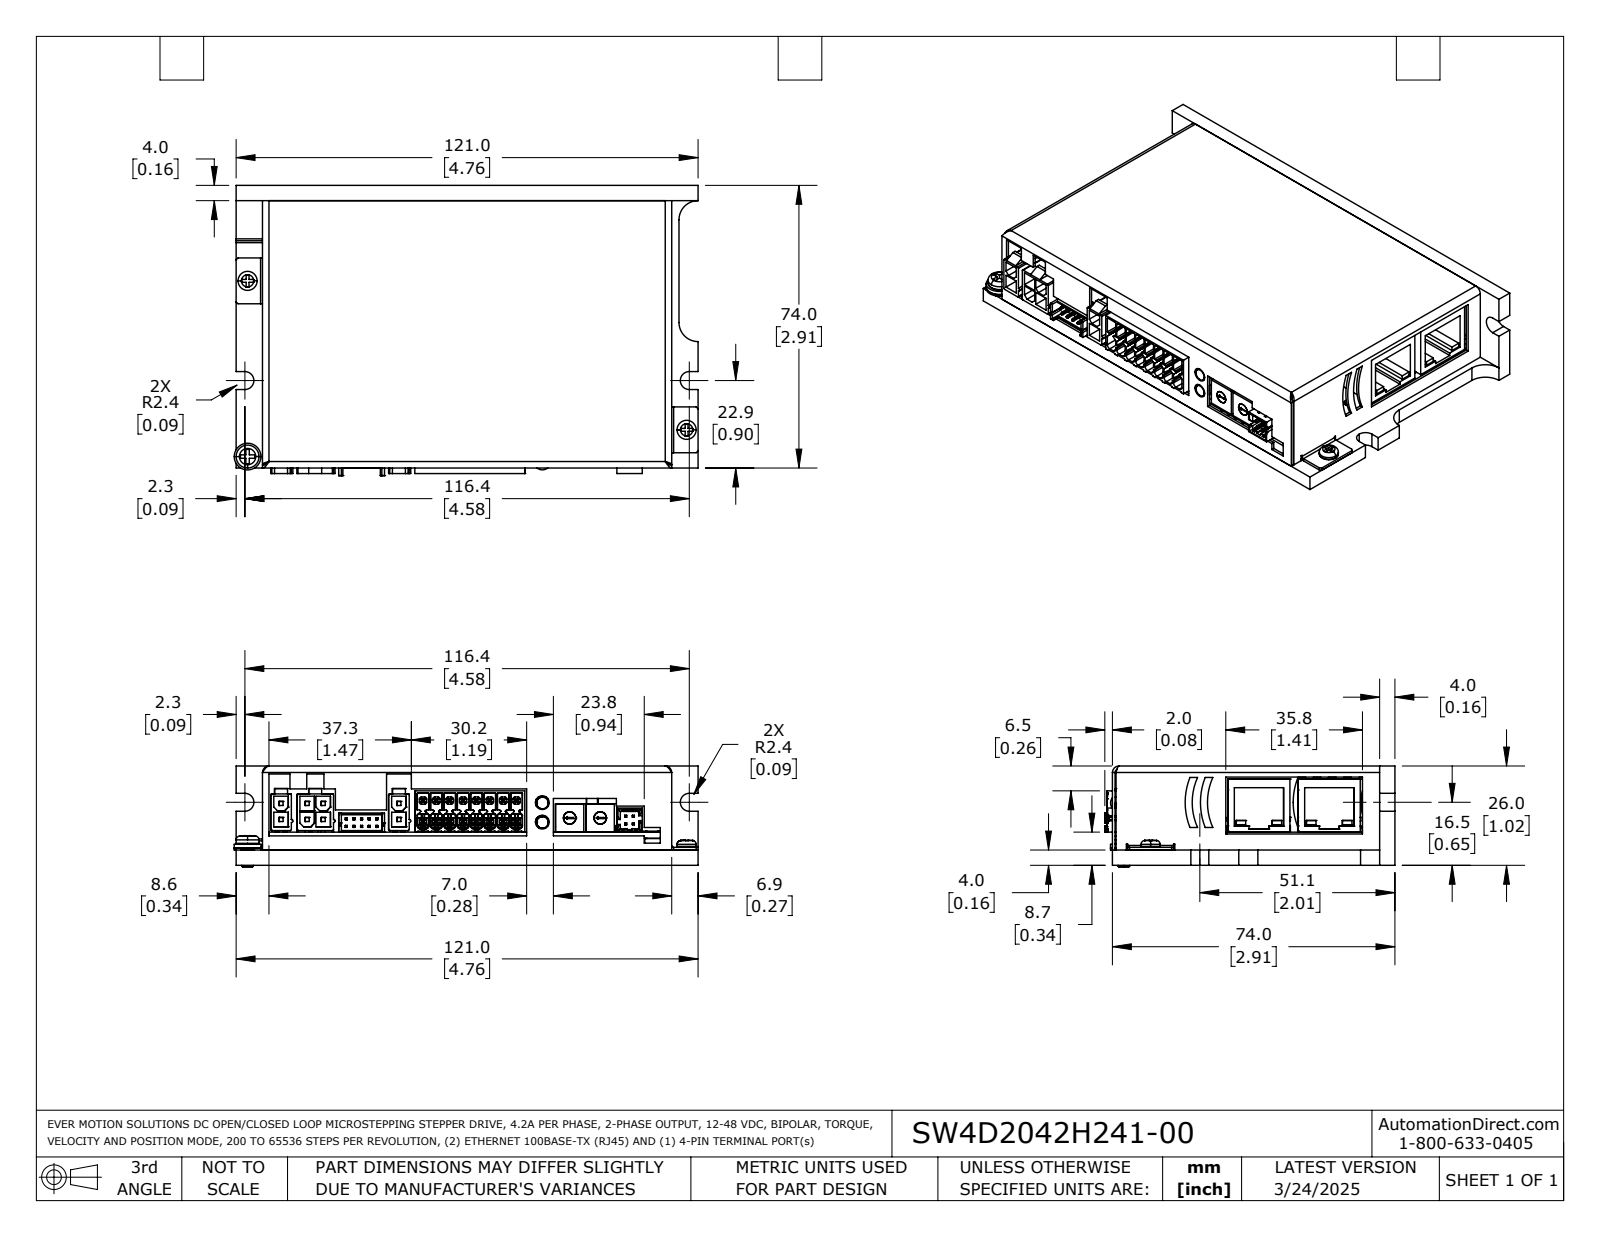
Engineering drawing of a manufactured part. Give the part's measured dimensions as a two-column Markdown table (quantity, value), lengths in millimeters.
| quantity | value |
| --- | --- |
| part name | SW4D2042H241-00C0680 |
| STEP written by | SolidWorks 2021 (AUTOMOTIVE_DESIGN) |
| units | millimeters |
| bodies | 21 solids, 3502 faces (2322 planar, 988 cylindrical, 192 other) |
| overall size | 121.5 × 76 × 26.5 |
| volume | 77 350 mm³ |
| surface area | 78 190 mm² |
| round holes (diameter × count) | 0.8 × 20, 0.9 × 16, 1.4 × 16, 0.9 × 14, 1 × 8, 1.3 × 8, 1.8 × 8, 3.2 × 7, 1.6 × 4, 2.5 × 4, 2.7 × 4, 3 × 4 |
| round bosses / shafts (diameter × count) | 5 × 2, 4.1 × 2, 3.8 × 2, 3.2 × 2, 3 × 2, 7 × 1, 6 × 1, 1.4 × 1 |
| partial cylindrical surfaces (radius × count) | 0.1 × 144, 0.3 × 19, 0.2 × 18, 0.9 × 18, 0.2 × 12, 0.2 × 10, 16 × 7, 17.9 × 7 |
| main face-to-face distances | 4, 0.7, 26, 22, 21.3, 25.3, 17.3, 3.1, 8.7, 4.7 |
| hole center spacings | 2.5, 2.8, 18.4, 4.6, 5.1, 6.8, 11.3, 3 |
